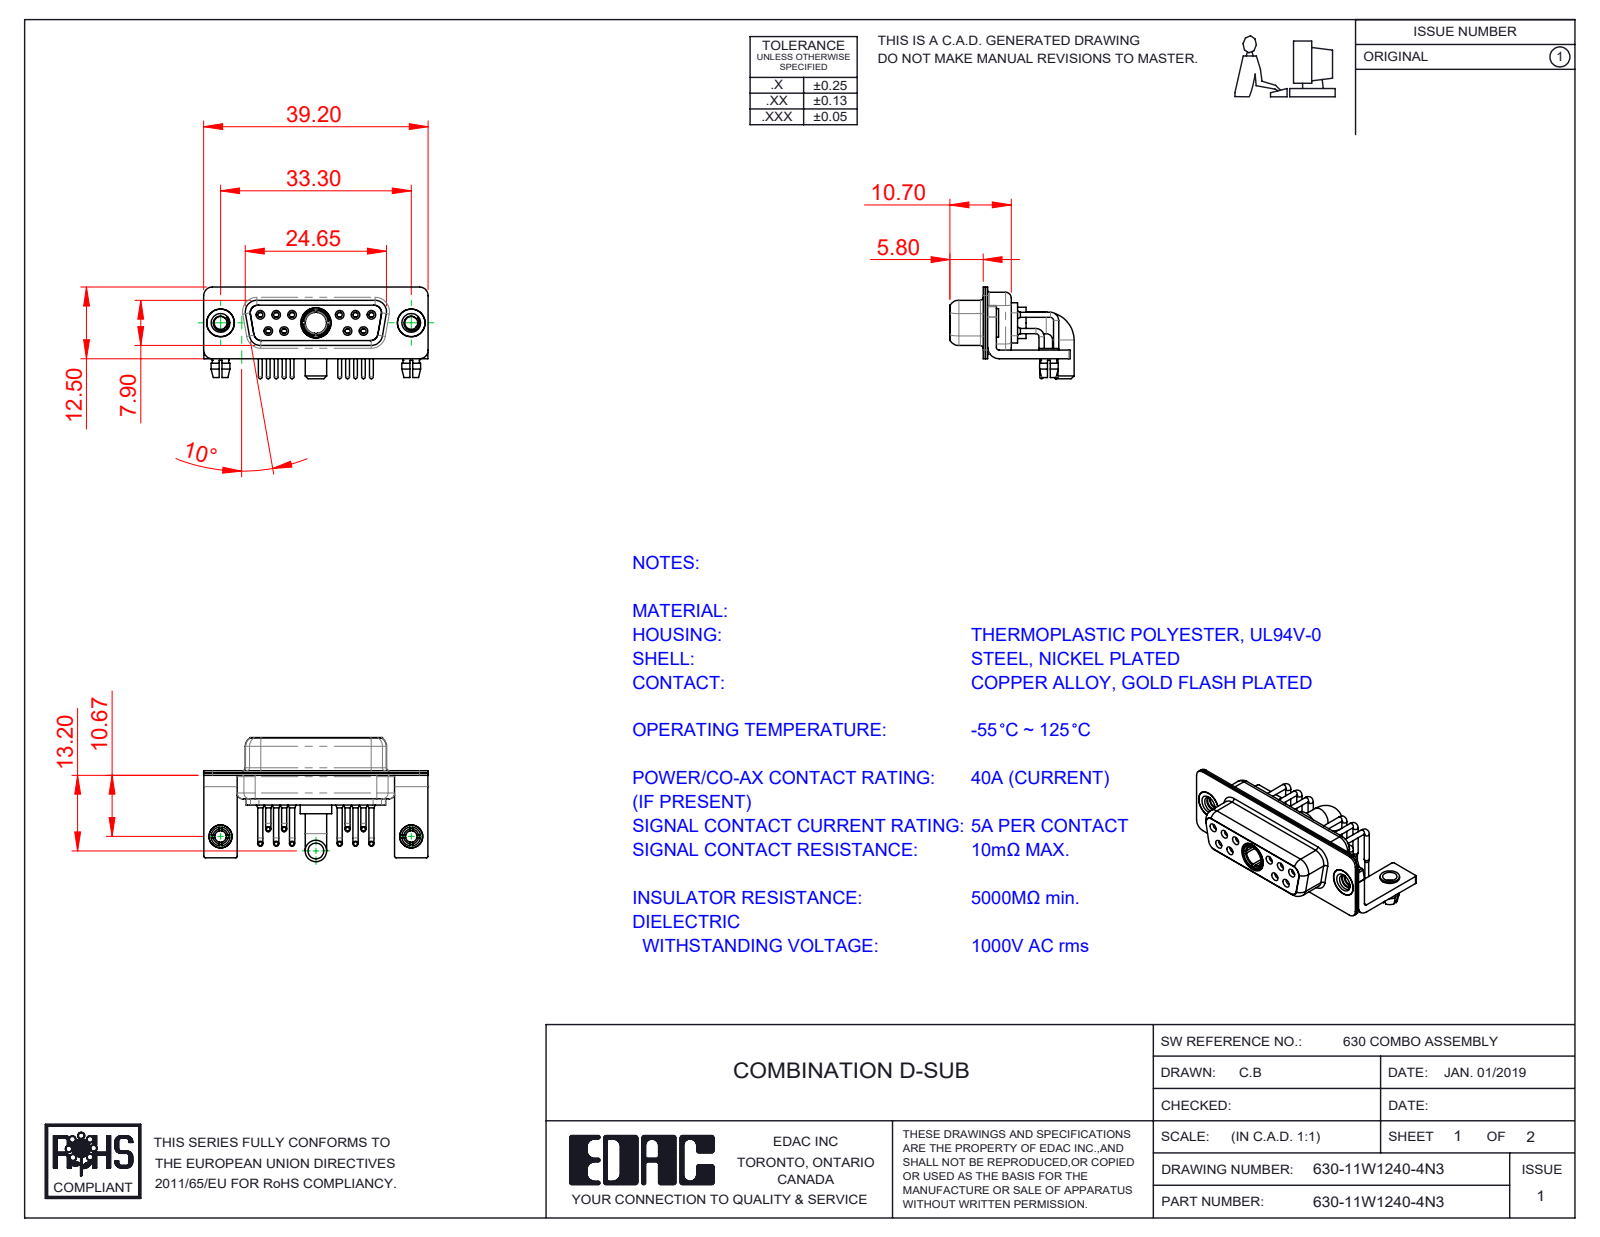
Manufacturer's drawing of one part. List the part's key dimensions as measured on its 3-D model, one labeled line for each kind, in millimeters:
Part name (STEP PRODUCT): 630Combo Contact Row 1; 630Combo Shell Rear_15 Contacts; 630Combo Shell Front_15 Contacts; 630Combo Threaded Rivet_3 (+6 more)
STEP written by: SolidWorks 2020 (CONFIG_CONTROL_DESIGN)
Units: millimetres
Bodies: 21 solids, 1019 faces (314 planar, 442 cylindrical, 263 other)
Overall size (bounding box): 39.2 × 21.68 × 16
Volume: 3 023 mm³ · Surface area: 7 113 mm²
Round holes (diameter × count): ⌀2 ×12, ⌀0.9 ×10, ⌀1.1 ×10, ⌀1.5 ×10, ⌀1.7 ×6, ⌀1.6 ×4, ⌀4.85 ×3, ⌀2.26 ×2, ⌀2.5 ×2, ⌀3.2 ×2, ⌀4 ×2, ⌀4.05 ×2
Round bosses / shafts (diameter × count): ⌀0.9 ×10, ⌀0.65 ×10, ⌀1.6 ×6, ⌀5 ×2, ⌀4.95 ×2, ⌀4.8 ×2, ⌀4 ×2, ⌀3.75 ×2
Partial cylindrical surfaces — rounded edges, fillets, slot ends (radius × count): R0.25 ×16, R1.5 ×16, R2 ×13, R1.35 ×12, R1.6 ×8, R0.5 ×5, R0.6 ×4, R0.65 ×4
Main face-to-face distances: 0.4, 0.8, 0.45, 1.4, 8.45, 1.8, 1.5, 8.9, 6.2, 2.3
Hole centre spacings: 3.16, 2.77, 13.85, 11.08, 16.62, 5.03, 5.04, 5.54
